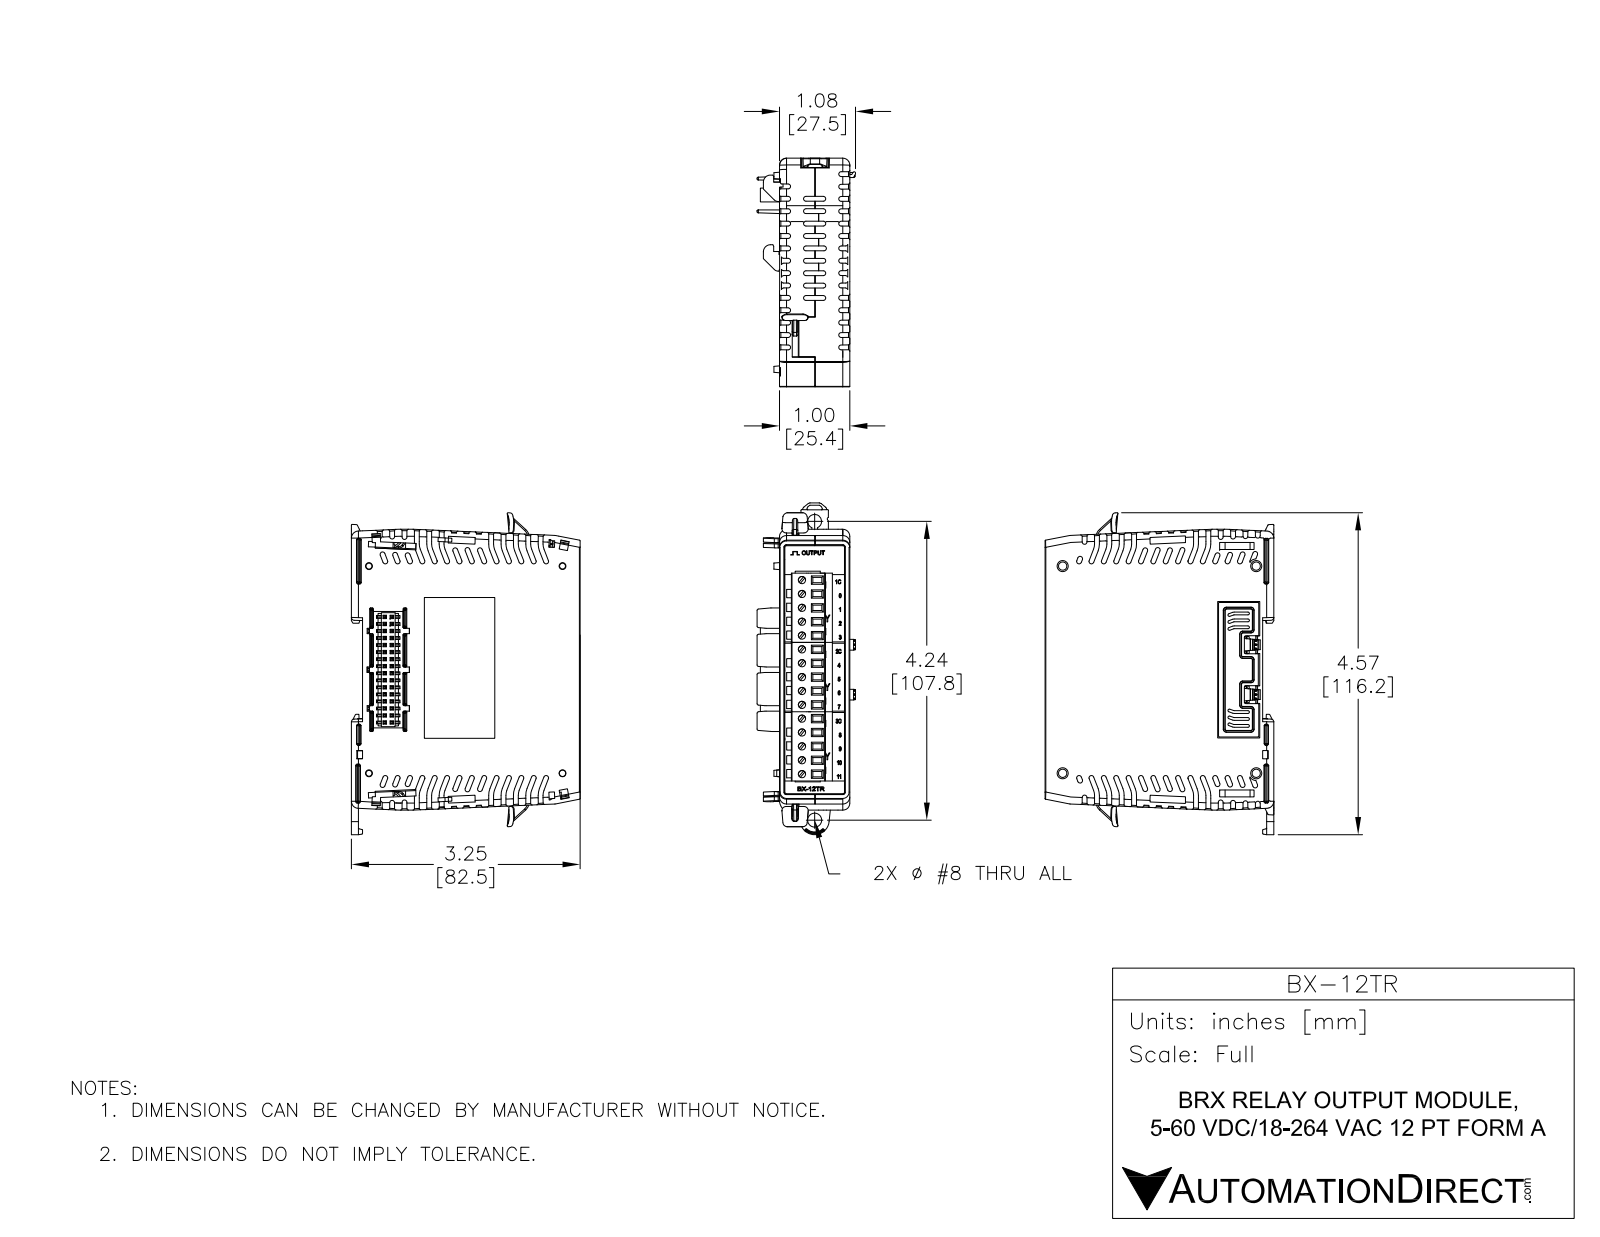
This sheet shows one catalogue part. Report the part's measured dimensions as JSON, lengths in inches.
{"part_name": "BX-12TR", "step_written_by": "SolidWorks 2017 (AUTOMOTIVE_DESIGN)", "units": "inches", "bodies": {"solids": 15, "faces": 3749, "planar": 2649, "cylindrical": 573, "other": 527}, "overall_size": [4.586, 3.311, 1.402], "volume_in3": 11.6, "surface_area_in2": 72.79, "round_holes": [[0.047, 2], [0.065, 2], [0.118, 2], [0.118, 2], [0.199, 1]], "round_bosses_or_shafts": [[0.062, 2], [0.059, 2]], "partial_cylinders_radius": [[0.005, 102], [0.01, 47], [0.02, 34], [0.005, 24], [0.008, 21], [0.122, 15], [0.117, 14], [0.039, 13]], "face_to_face_distances": [1, 3.211, 0.1, 3.22, 0.475, 0.157, 3.053, 3.063, 0.787, 0.63], "hole_center_spacings": [0.1, 0.824, 0.919, 1.3, 2.093, 2.193, 2.585, 2.617]}
